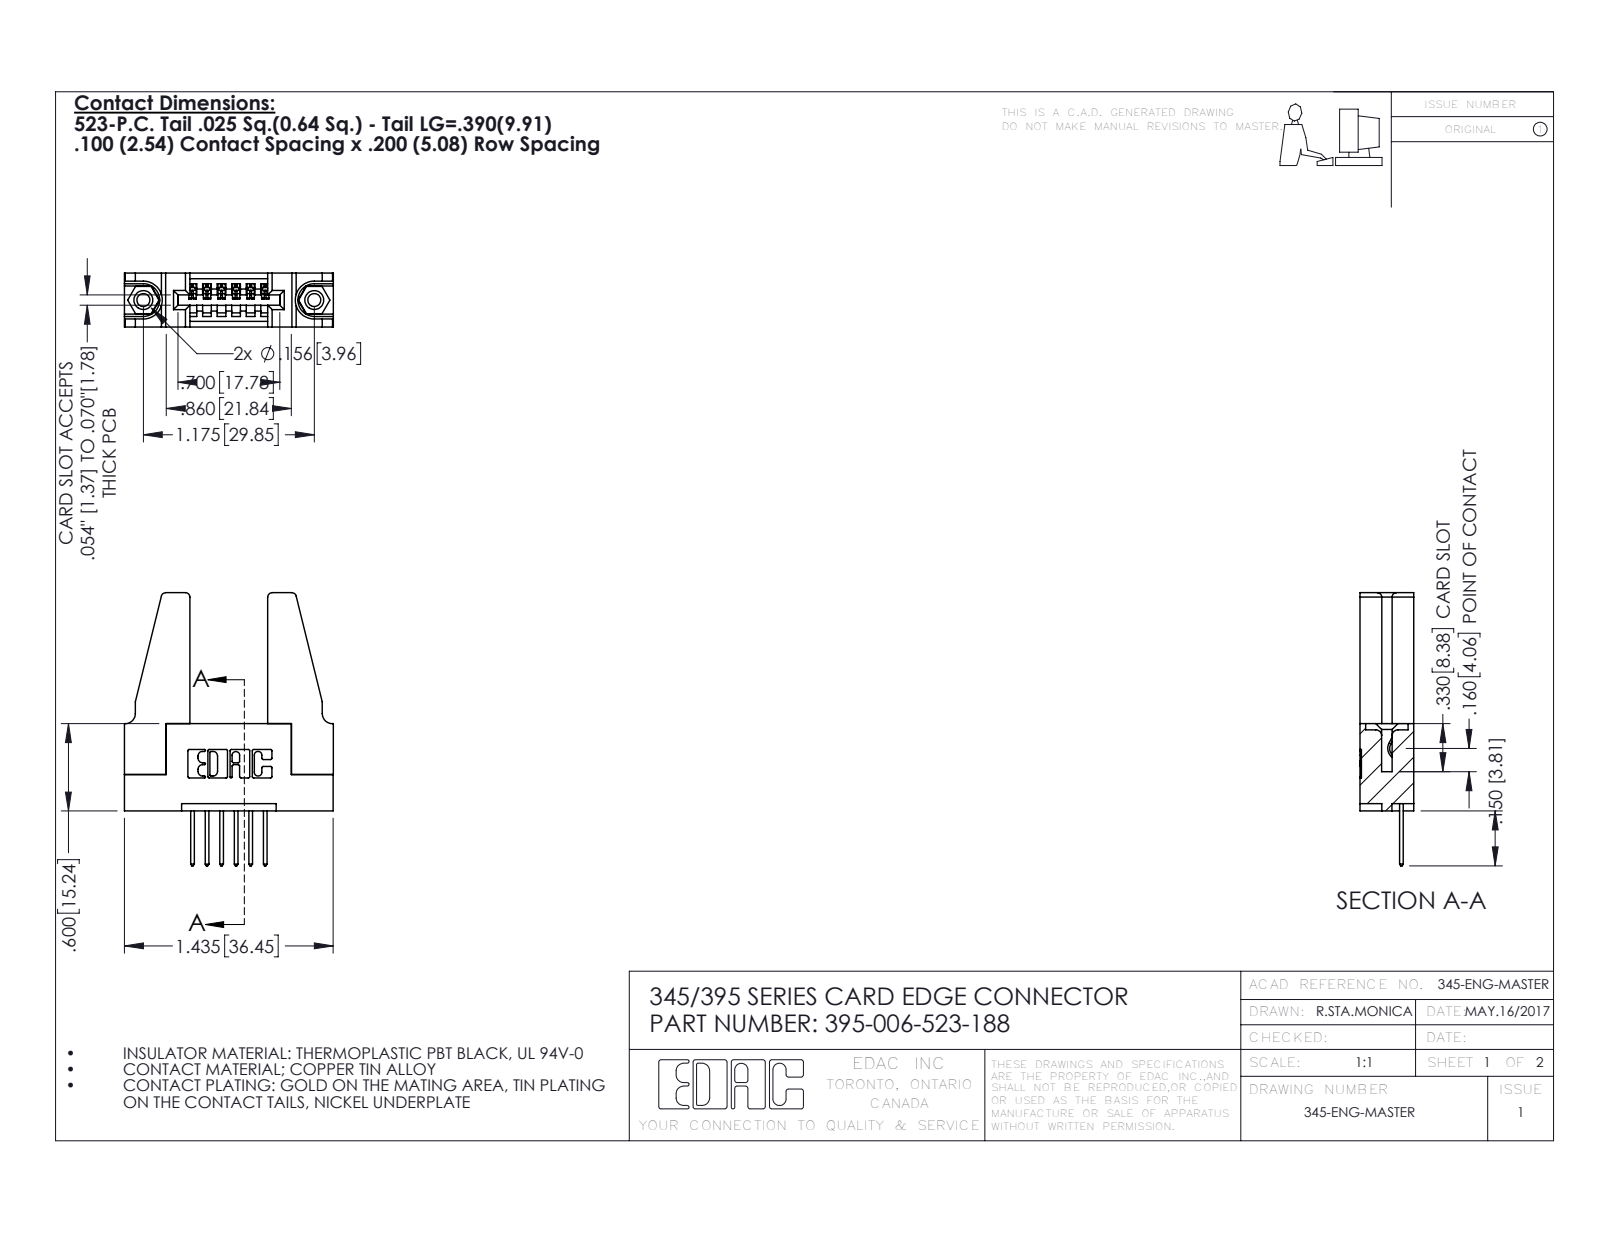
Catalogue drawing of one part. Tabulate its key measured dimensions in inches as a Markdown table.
| quantity | value |
| --- | --- |
| part name | 395-006-523-188; 345-292-001_345-293-123; 345 Part_Flush Mounting Lugs - 0.156 Dia-TH; 345-250-001_345-250-001-102 (+1 more) |
| STEP written by | SolidWorks 2016 (CONFIG_CONTROL_DESIGN) |
| units | inches |
| bodies | 11 solids, 598 faces (392 planar, 190 cylindrical, 16 other) |
| overall size | 1.877 × 1.436 × 0.37 |
| volume | 0.392 in³ |
| surface area | 10.63 in² |
| round holes (diameter × count) | 0.089 × 2, 0.125 × 2, 0.156 × 2, 0.064 × 1 |
| round bosses / shafts (diameter × count) | 0.155 × 2 |
| partial cylindrical surfaces (radius × count) | 0.01 × 22, 0.006 × 12, 0.01 × 12, 0.03 × 8, 0.007 × 6, 0.031 × 6, 0.026 × 3, 0.031 × 2 |
| main face-to-face distances | 0.37, 0.2, 0.072, 0.298, 0.698, 0.15, 0.148, 0.35, 0.098, 0.272 |
| hole center spacings | 0.27, 0.946, 1.175 |
